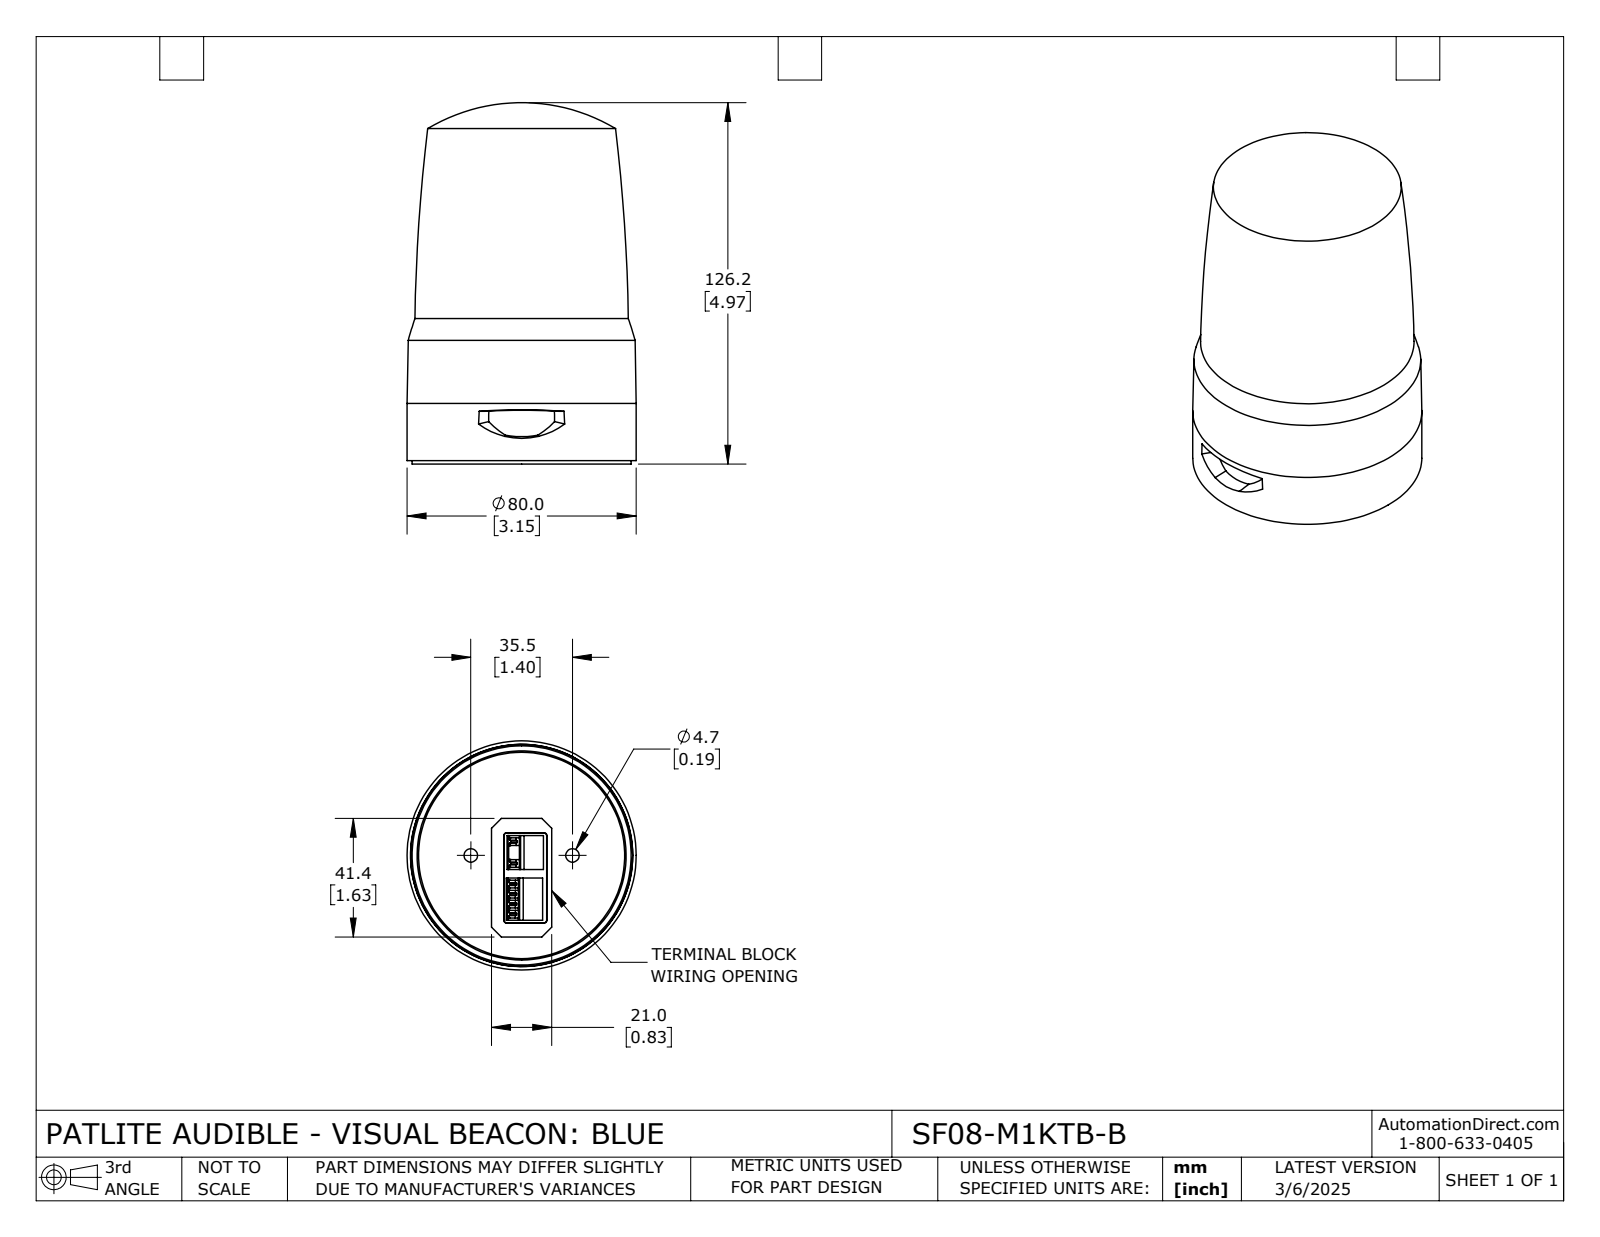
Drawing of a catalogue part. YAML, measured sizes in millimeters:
part_name: "SF08-M1KTB-B"
step_written_by: "SolidWorks 2024 (CONFIG_CONTROL_DESIGN)"
units: millimeters
bodies: {solids: 2, faces: 262, planar: 168, cylindrical: 32, other: 62}
overall_size: [126.2, 80, 80]
volume: 488153
surface_area: 54584
round_holes:
  - {diameter: 4.7, count: 2}
  - {diameter: 12.2, count: 2}
  - {diameter: 73, count: 1}
round_bosses_or_shafts:
  - {diameter: 80, count: 1}
  - {diameter: 76.5, count: 1}
  - {diameter: 74.6, count: 1}
  - {diameter: 72, count: 1}
partial_cylinders:
  - {radius: 1, count: 4}
  - {radius: 0.3, count: 2}
  - {radius: 34.6, count: 1}
  - {radius: 35, count: 1}
face_to_face_distances: [15.7, 6.3, 9.4, 3, 5.1, 14.5, 3.15, 6.15, 1.3, 12.45]
hole_center_spacings: [17.75, 35.5]
